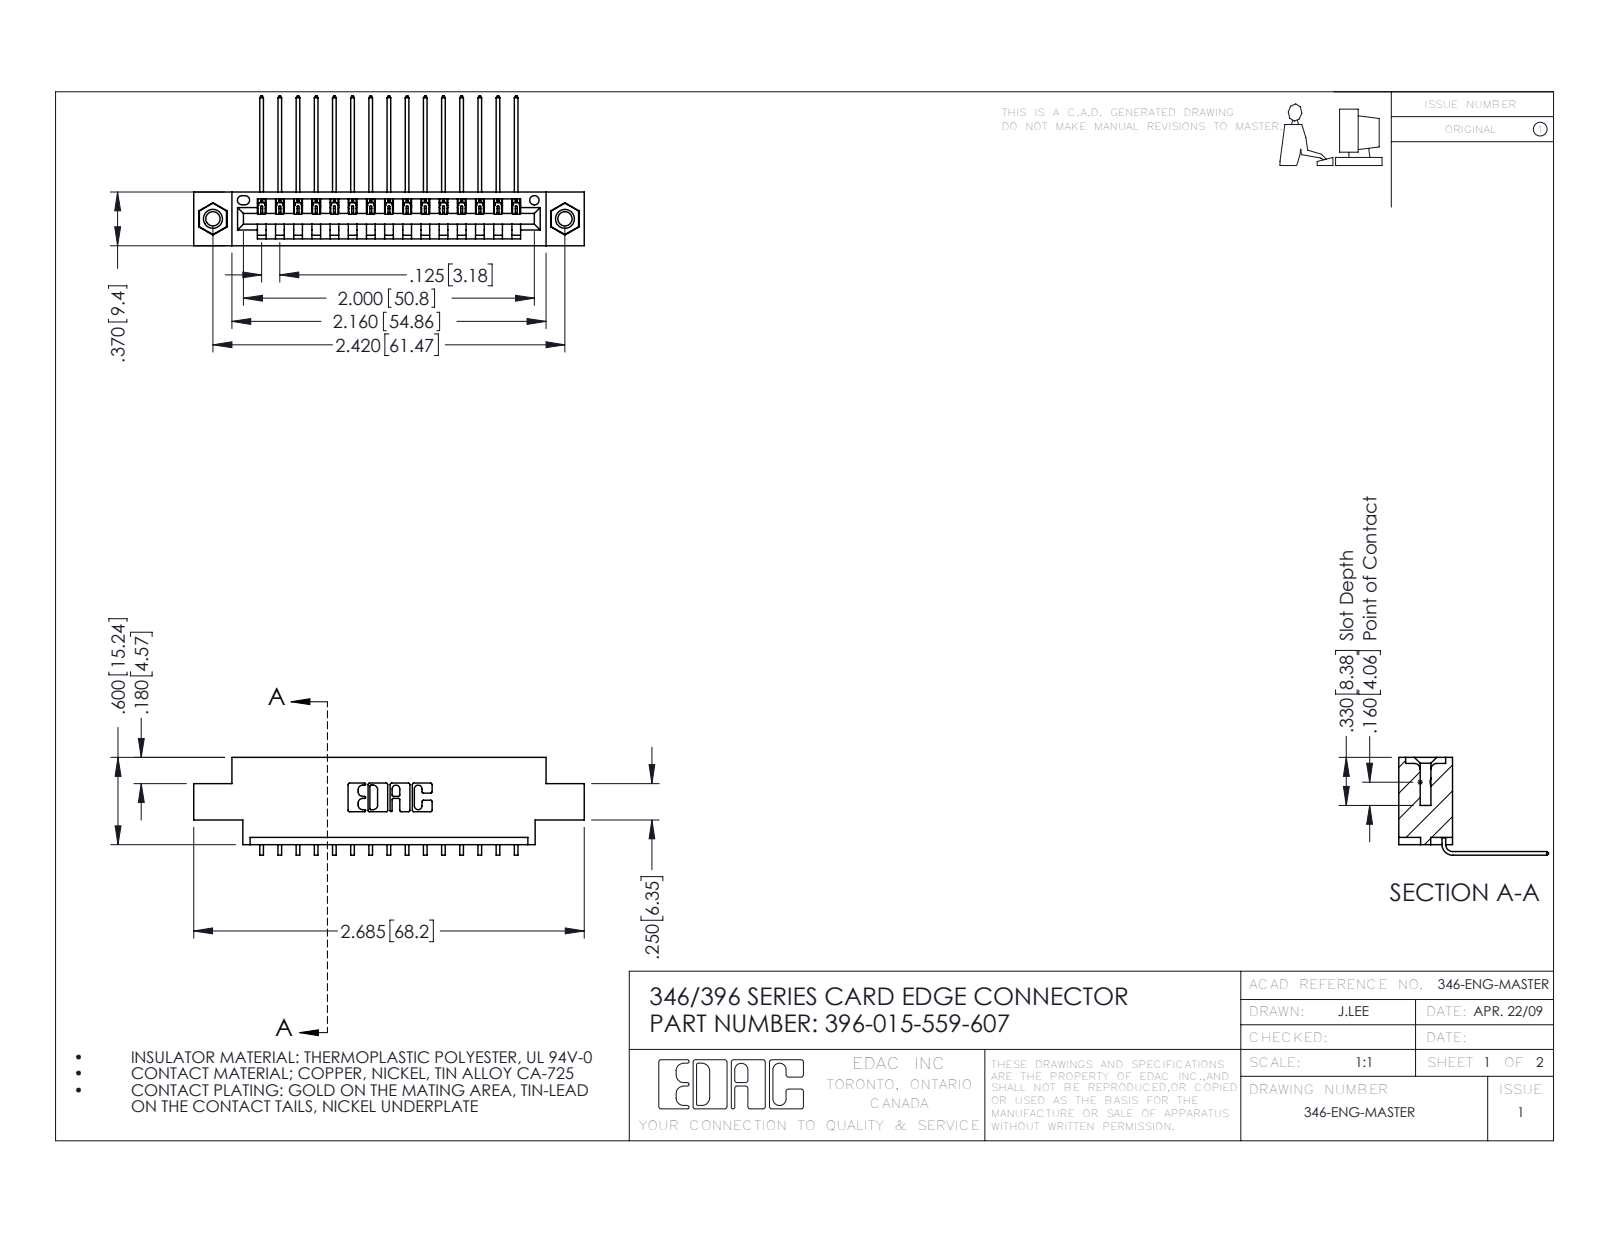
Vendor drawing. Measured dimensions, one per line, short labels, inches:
name: 345-292-001_558 559 Tail - 1; 346 Part_0.170 Offset - 0.156 Dia-TI; 396-015-559-607; 345-250-001_345-250-005-103
written by: SolidWorks 2016 (CONFIG_CONTROL_DESIGN)
unit: in
bodies: 18 solids, 1086 faces (742 planar, 328 cylindrical, 16 other)
size: 2.685 × 1.03 × 0.673
volume: 0.38 in³; area: 12.37 in²
holes: 2× ⌀0.098, 2× ⌀0.125, 2× ⌀0.156, 1× ⌀0.064
bosses: 2× ⌀0.155
rounds: 30× R0.006, 22× R0.01, 6× R0.007, 6× R0.031, 3× R0.026, 2× R0.031, 2× R0.04, 1× R0.014
face distances: 0.048, 0.37, 0.322, 0.25, 0.025, 0.072, 0.222, 0.148, 0.1, 0.174
hole spacings: 0.246, 2.213, 2.42
